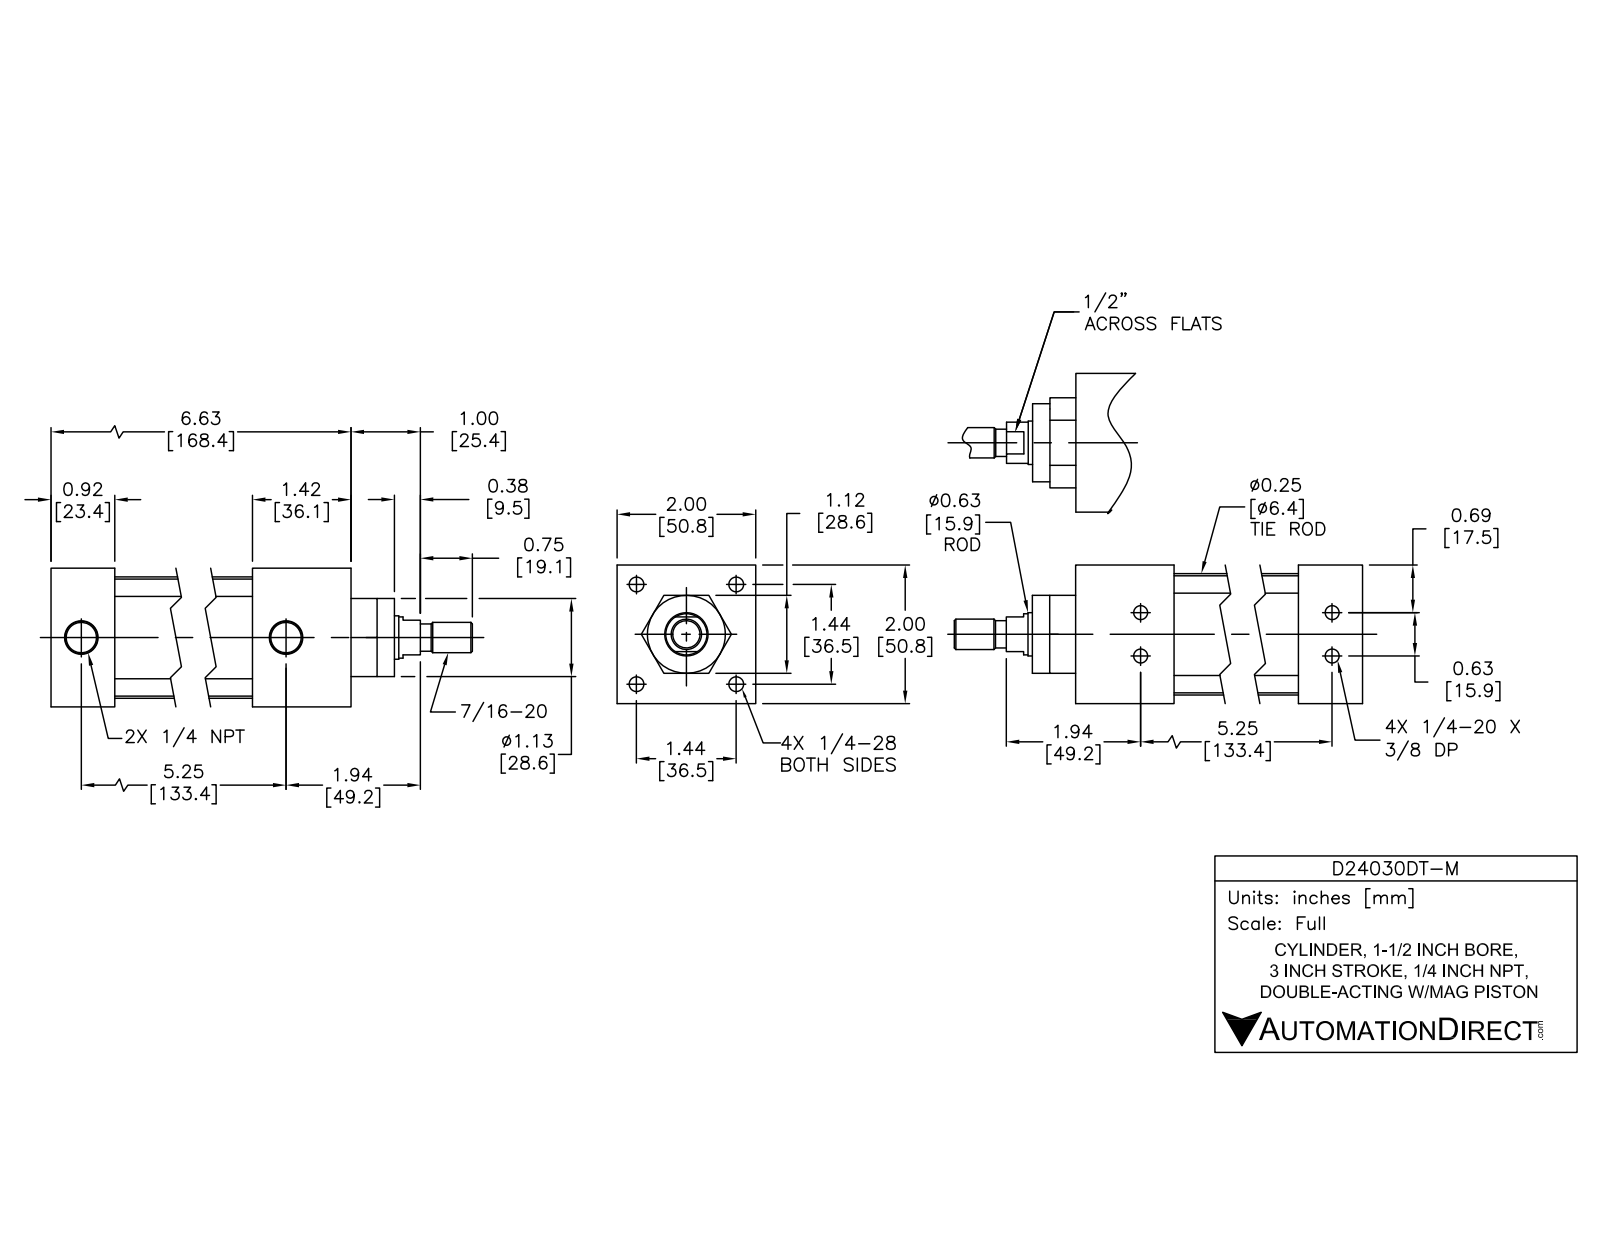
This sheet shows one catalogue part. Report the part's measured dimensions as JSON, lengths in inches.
{"part_name": "D24030DT-M; D24030DT-M BODY; D24030DT-M PISTON", "step_written_by": "SolidWorks 2015 (AUTOMOTIVE_DESIGN)", "units": "inches", "bodies": {"solids": 12, "faces": 303, "planar": 99, "cylindrical": 114, "other": 90}, "overall_size": [8.371, 2, 2], "volume_in3": 15.98, "surface_area_in2": 137.9, "round_holes": [[0.196, 4], [0.211, 4], [0.281, 4], [0.406, 4], [0.297, 2], [0.477, 2], [0.625, 1], [0.628, 1], [1.5, 1]], "round_bosses_or_shafts": [[0.39, 4], [0.25, 4], [0.222, 4], [1.75, 1], [1.497, 1], [1.121, 1], [0.622, 1], [0.59, 1]], "partial_cylinders_radius": [[0.2, 4]], "face_to_face_distances": [2, 6.621, 1.42, 5.201, 5.701, 4.281, 0.92, 1.121, 5.601, 4.181], "hole_center_spacings": [0.313, 1.014, 1.434, 0.625, 2.028, 5.247, 5.255, 5.256]}
